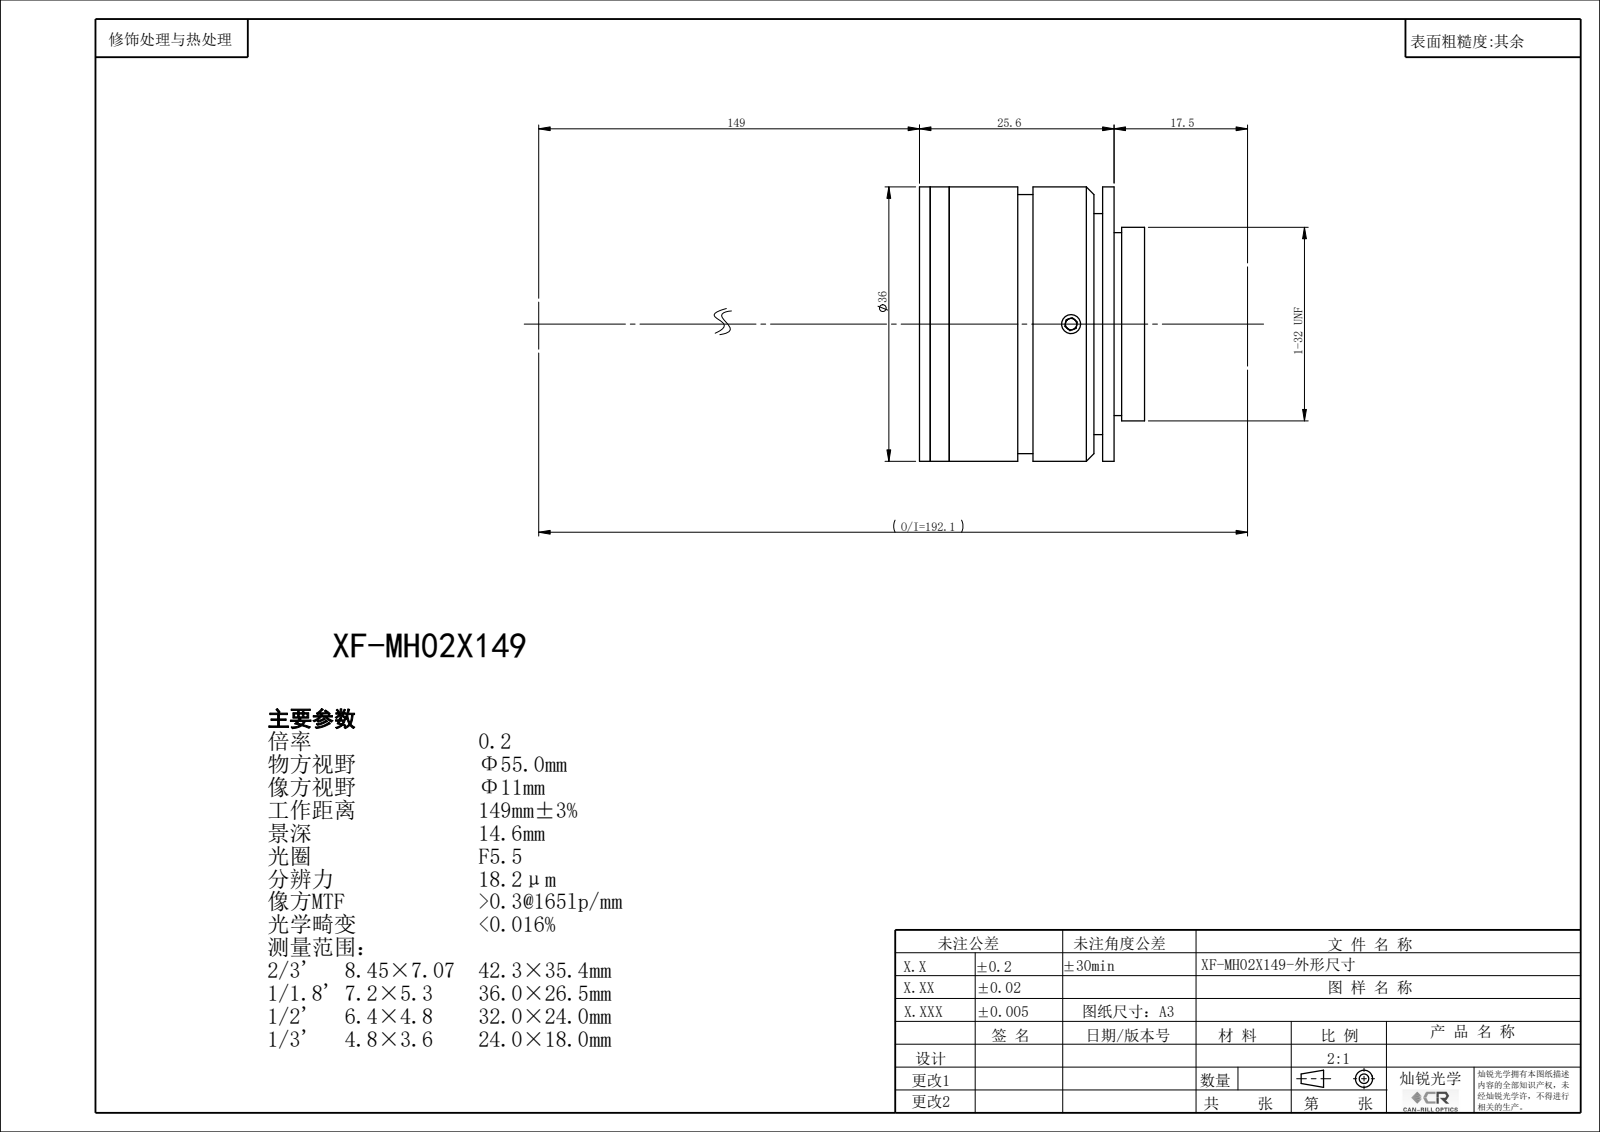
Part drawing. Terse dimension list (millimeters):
name: XF-NH02X149
written by: SolidWorks 2014 (CONFIG_CONTROL_DESIGN)
unit: mm
bodies: 0 solids, 93 faces (39 planar, 37 cylindrical, 17 other)
size: 36 × 36 × 29.4
holes: 2× ⌀1, 1× ⌀8, 1× ⌀10.4, 1× ⌀20, 1× ⌀21
bosses: 1× ⌀36, 1× ⌀25.4, 1× ⌀4.5
rounds: 5× R25, 1× R2.5
face distances: 2.5, 7, 1.4, 1, 3.9, 14, 10.5, 21, 8, 25.4
hole spacings: 11.5, 23
